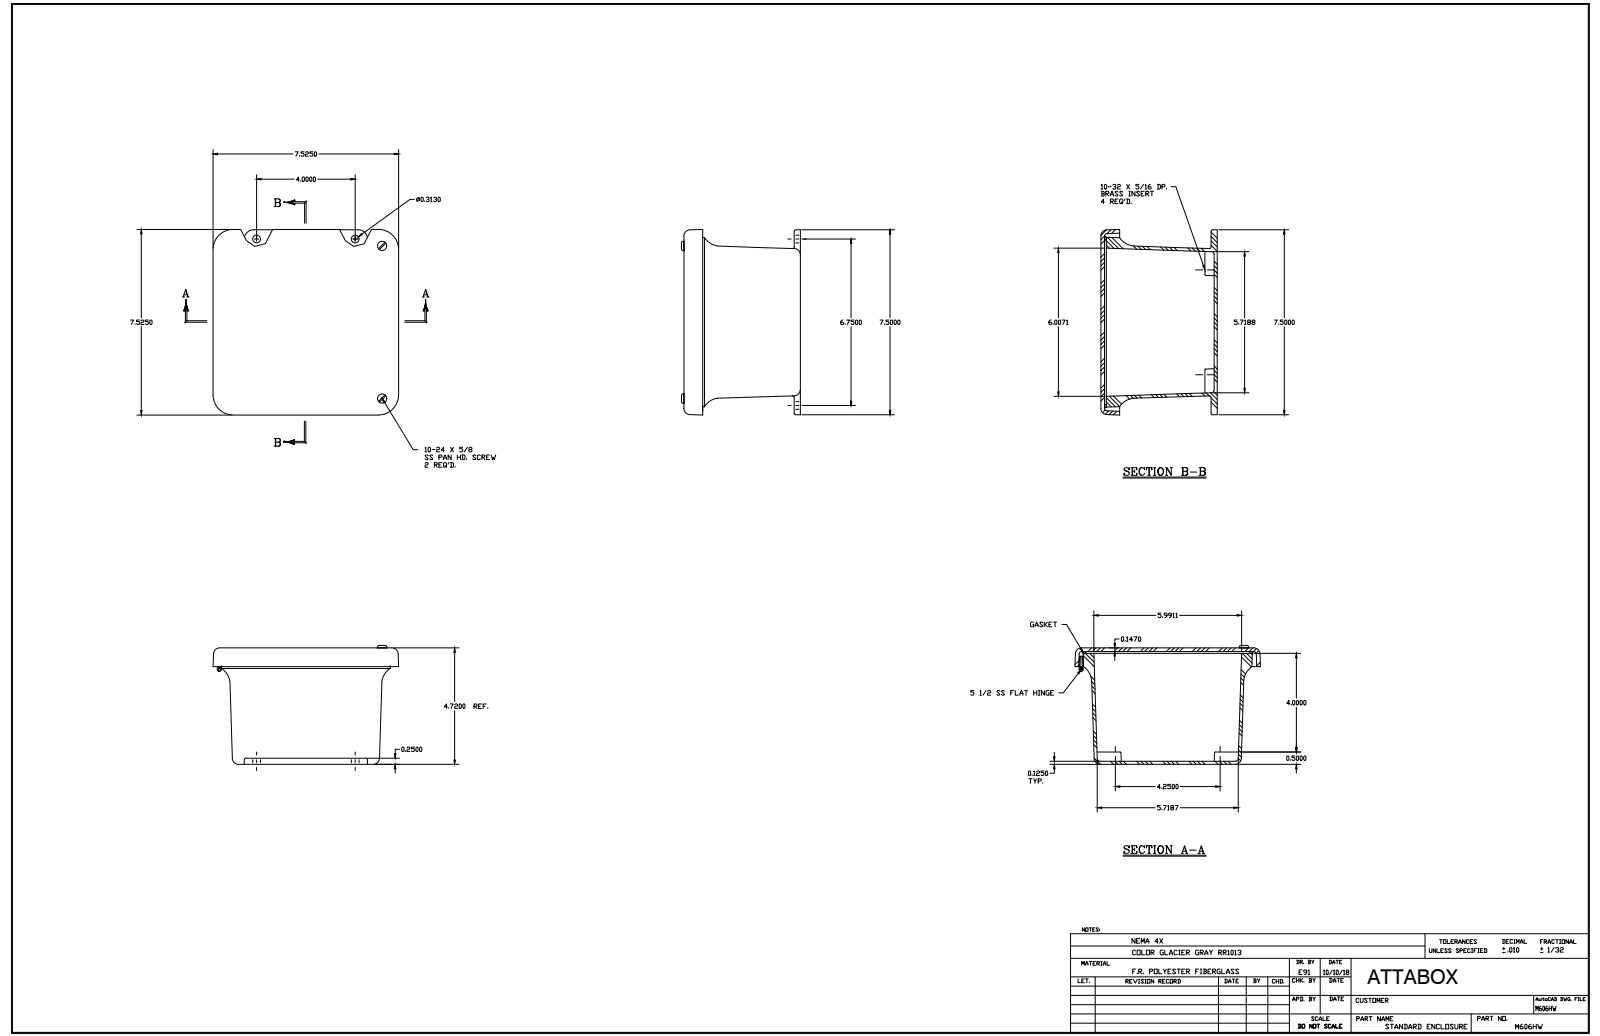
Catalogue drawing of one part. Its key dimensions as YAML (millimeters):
part_name: "M606HW"
step_written_by: "SolidWorks 2018 (AUTOMOTIVE_DESIGN)"
units: millimeters
bodies: {solids: 19, faces: 657, planar: 200, cylindrical: 251, other: 206}
overall_size: [191.8, 191.1, 126.3]
volume: 619300
surface_area: 324200
round_holes:
  - {diameter: 3.3, count: 5}
  - {diameter: 3.6, count: 5}
  - {diameter: 3.9, count: 5}
  - {diameter: 4, count: 4}
  - {diameter: 5.5, count: 4}
  - {diameter: 3.7, count: 2}
  - {diameter: 2.2, count: 1}
  - {diameter: 2.2, count: 1}
round_bosses_or_shafts:
  - {diameter: 6.9, count: 6}
  - {diameter: 6.4, count: 5}
  - {diameter: 3.2, count: 5}
  - {diameter: 4.8, count: 2}
  - {diameter: 4, count: 2}
  - {diameter: 3.9, count: 1}
  - {diameter: 3.9, count: 1}
partial_cylinders:
  - {radius: 0.8, count: 20}
  - {radius: 6.4, count: 12}
  - {radius: 3.2, count: 8}
  - {radius: 5.1, count: 7}
  - {radius: 1.6, count: 4}
  - {radius: 9.5, count: 4}
  - {radius: 19.1, count: 4}
  - {radius: 1.6, count: 2}
face_to_face_distances: [3.7, 119.2, 123, 3.2, 116.1, 119.8, 3.9, 114.3, 5.5, 117.5]
hole_center_spacings: [134.8, 34.8, 63.5, 108, 157.1, 187.5, 12.7, 50.8]
